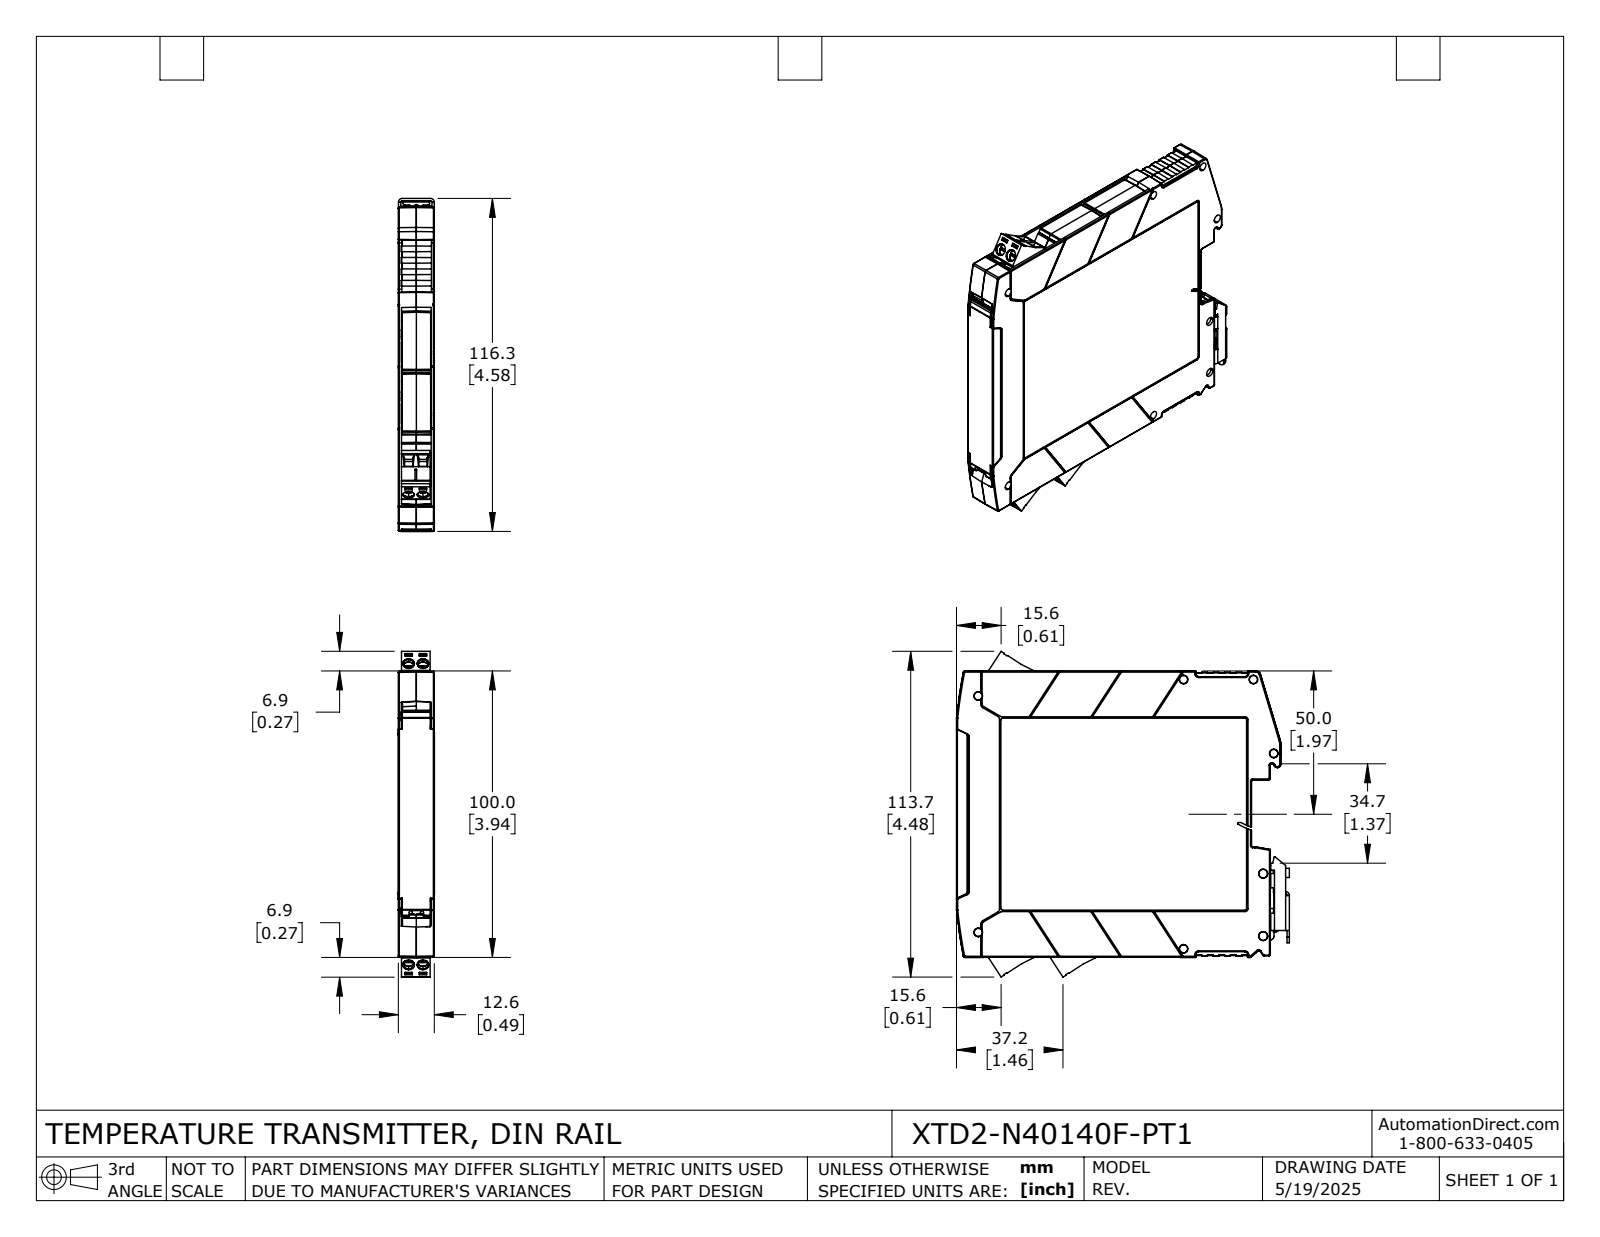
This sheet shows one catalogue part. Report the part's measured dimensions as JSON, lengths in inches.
{"part_name": "XTD2-N40140F-PT1", "step_written_by": "SolidWorks 2024 (AUTOMOTIVE_DESIGN)", "units": "inches", "bodies": {"solids": 14, "faces": 3337, "planar": 1910, "cylindrical": 596, "other": 831}, "overall_size": [4.577, 4.478, 0.496], "volume_in3": 2.41, "surface_area_in2": 101.5, "round_holes": [[0.063, 6], [0.11, 6], [0.152, 6], [0.159, 6]], "round_bosses_or_shafts": [[0.156, 6], [0.098, 6], [0.059, 2], [0.053, 2]], "partial_cylinders_radius": [[0.008, 89], [0.012, 78], [0.02, 71], [0.039, 22], [0.004, 20], [0.016, 13], [0.006, 12], [0.028, 8]], "face_to_face_distances": [0.049, 0.445, 0.494, 0.396, 0.043, 0.451, 0.402, 0.031, 0.198, 0.247], "hole_center_spacings": [0.197, 0.464, 0.504, 0.713, 0.739]}
